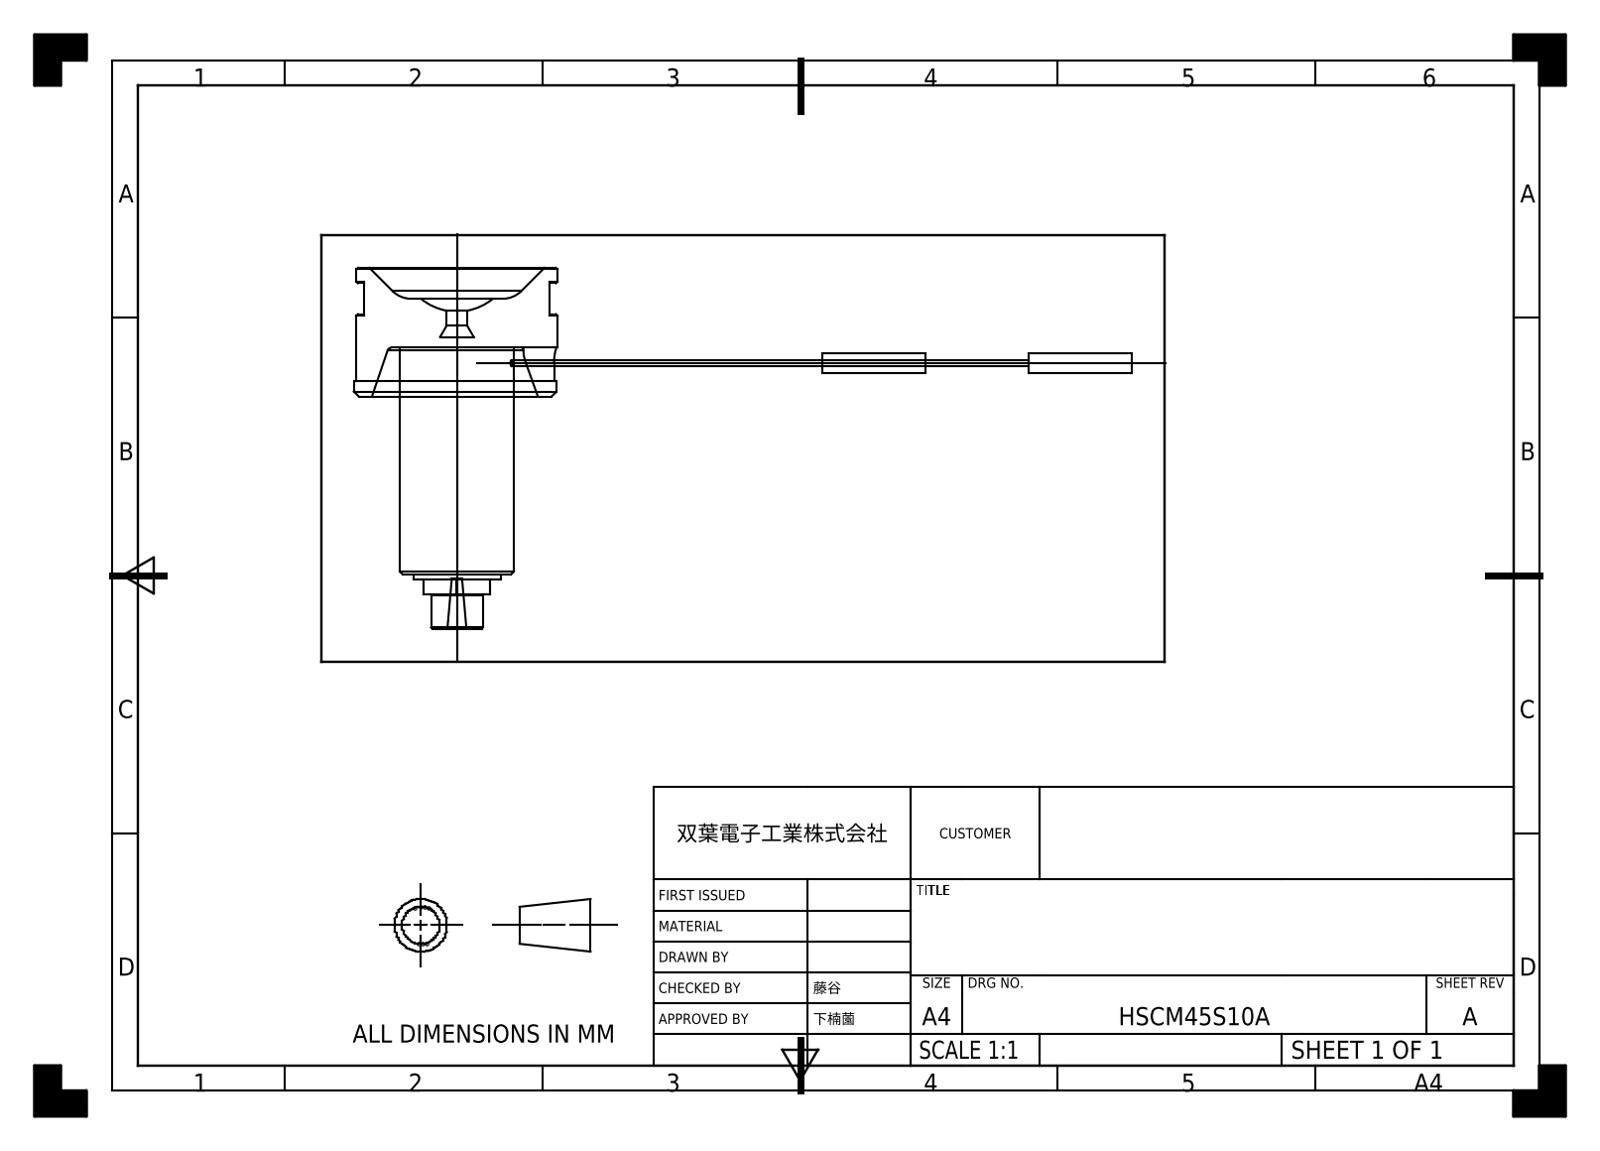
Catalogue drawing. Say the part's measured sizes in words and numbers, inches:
The part is named "HSCM45S10A". Its 3-D file was written by "SIEMENS PLM Software NX 2023 (AUTOMOTIVE_DESIGN)". It is 1 solid with 63 faces: 29 planar, 18 cylindrical and 16 other. Overall it measures 5.945 by 2.756 by 1.575 inches. Its volume is 2.272 cubic inches and its surface area 17.1 square inches. Round holes: 1 of diameter 0.157. Round bosses or shafts: 2 of diameter 0.157, 2 of diameter 0.047, 1 of diameter 1.575, 1 of diameter 1.535, 1 of diameter 0.866, 1 of diameter 0.665, 1 of diameter 0.394. Partial cylindrical surfaces (rounded edges, fillets, slot ends): 2 of radius 0.118, 1 of radius 0.293. The main face-to-face distances are 0.374, 0.984, 0.61, 2.146, 1.772, 2.343, 1.732, 1.358, 0.118, 0.236.
